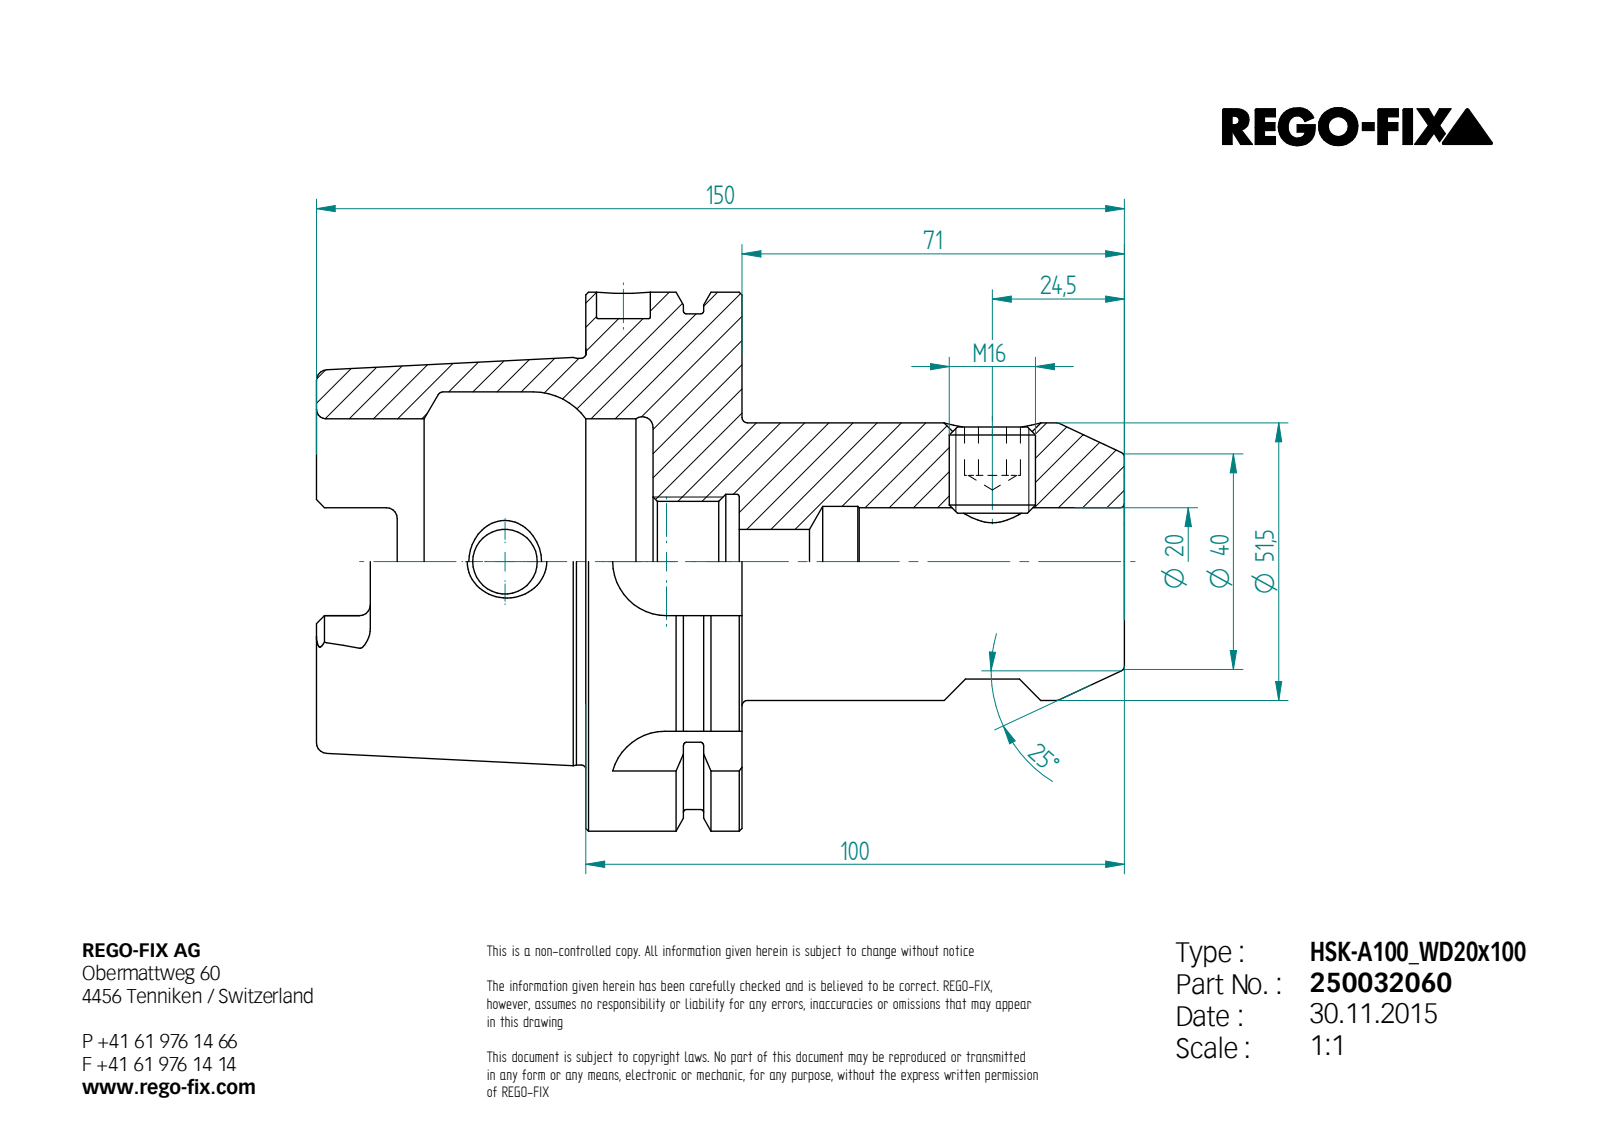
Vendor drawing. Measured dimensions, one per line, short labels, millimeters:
written by: Unknown (AUTOMOTIVE_DESIGN)
unit: mm
bodies: 2 solids, 144 faces (52 planar, 36 cylindrical, 56 other)
size: 150 × 100 × 100
volume: 376 087 mm³; area: 65 746 mm²
holes: 2× ⌀12, 1× ⌀8.5, 1× ⌀10, 1× ⌀13.84, 1× ⌀20, 1× ⌀20.5, 1× ⌀22.38, 1× ⌀25, 1× ⌀53, 1× ⌀63
bosses: 1× ⌀100, 1× ⌀92, 1× ⌀75.46, 1× ⌀51.5, 1× ⌀16
rounds: 6× R2, 4× R4.88, 2× R10, 1× R11
face distances: 29, 12.5, 16.5, 100, 87.5, 71, 50, 62.5, 79, 150
hole spacings: 68.5
